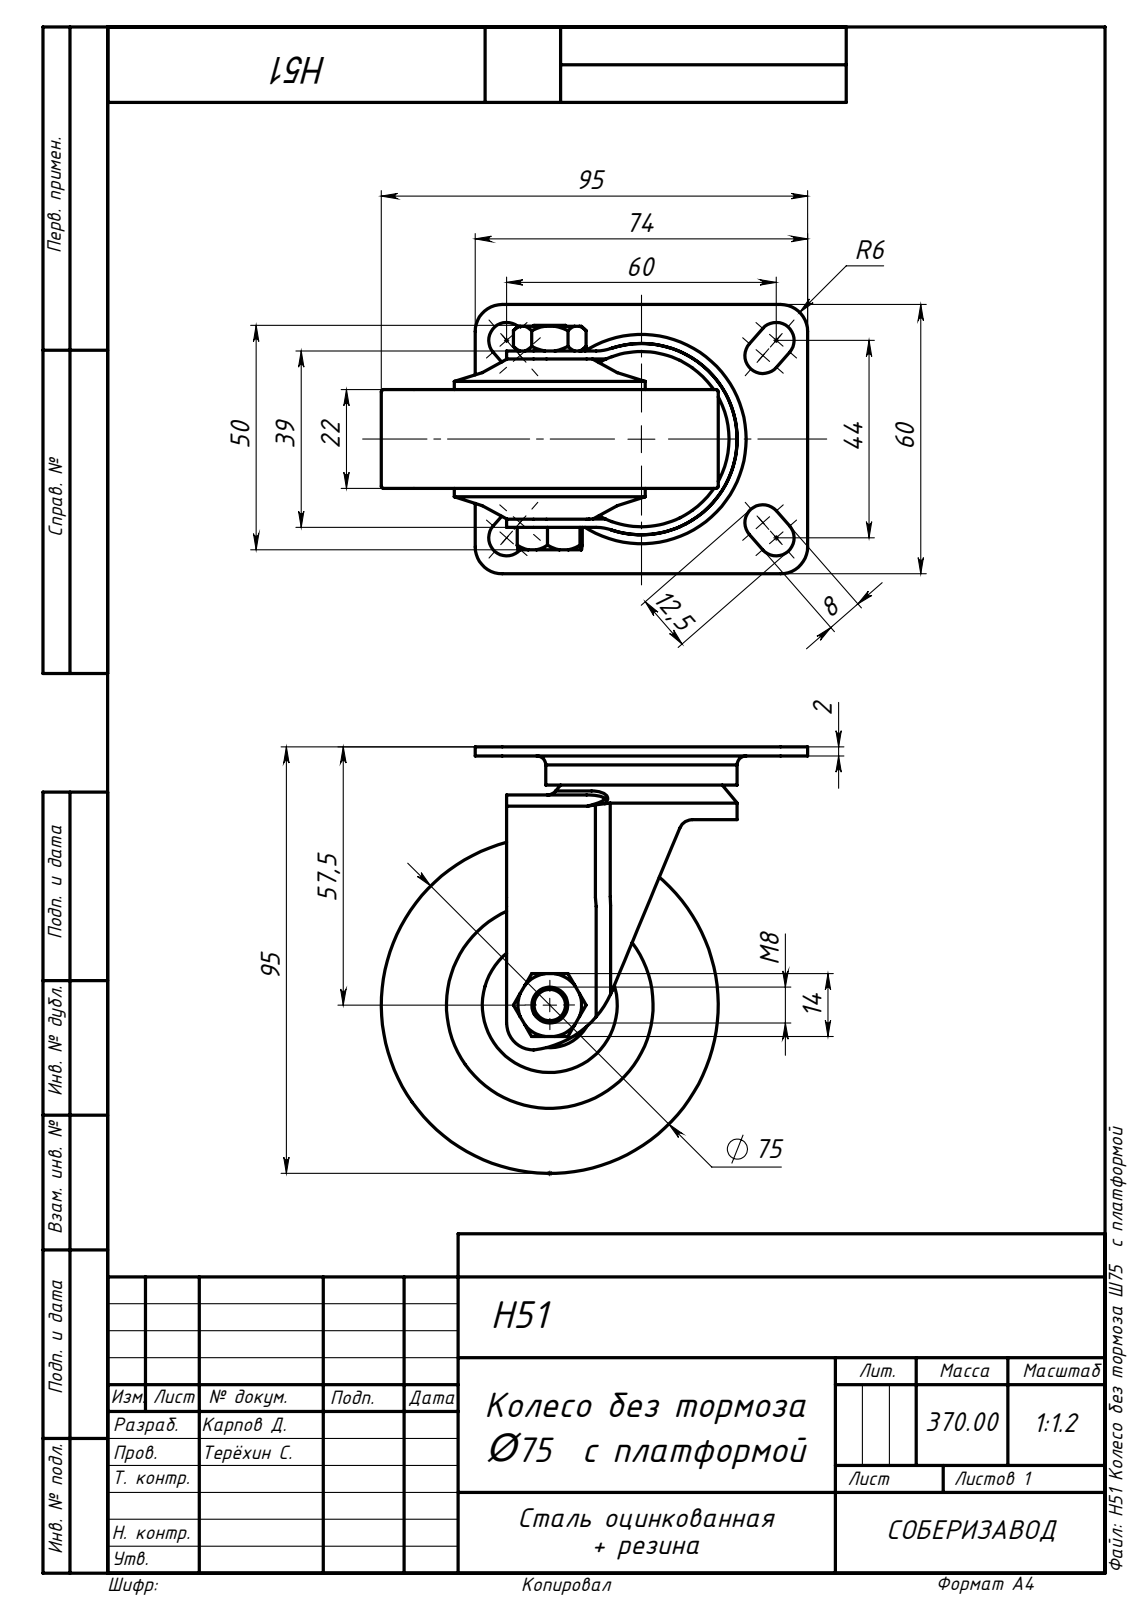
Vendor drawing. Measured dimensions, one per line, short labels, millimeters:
name: Сборка1; H51 Гайка_00; H51 Ось_00; H51 Болт_00 (+5 more)
written by: SolidWorks 2022 (AUTOMOTIVE_DESIGN)
unit: mm
bodies: 8 solids, 235 faces (70 planar, 83 cylindrical, 82 other)
size: 98.45 × 95 × 67.17
volume: 108 290 mm³; area: 53 007 mm²
holes: 1× ⌀7, 1× ⌀8, 1× ⌀8.2, 1× ⌀12, 1× ⌀12.5, 1× ⌀20, 1× ⌀41.5, 1× ⌀52
bosses: 1× ⌀75, 1× ⌀54.5, 1× ⌀42.5, 1× ⌀35, 1× ⌀30, 1× ⌀22, 1× ⌀15
rounds: 8× R4.2, 5× R6, 4× R2.5, 4× R10, 1× R3, 1× R19.51, 1× R21.31, 1× R21.5
face distances: 2, 6.5, 5, 22, 1.8, 6.82, 28.82, 8.5, 4, 15.82
